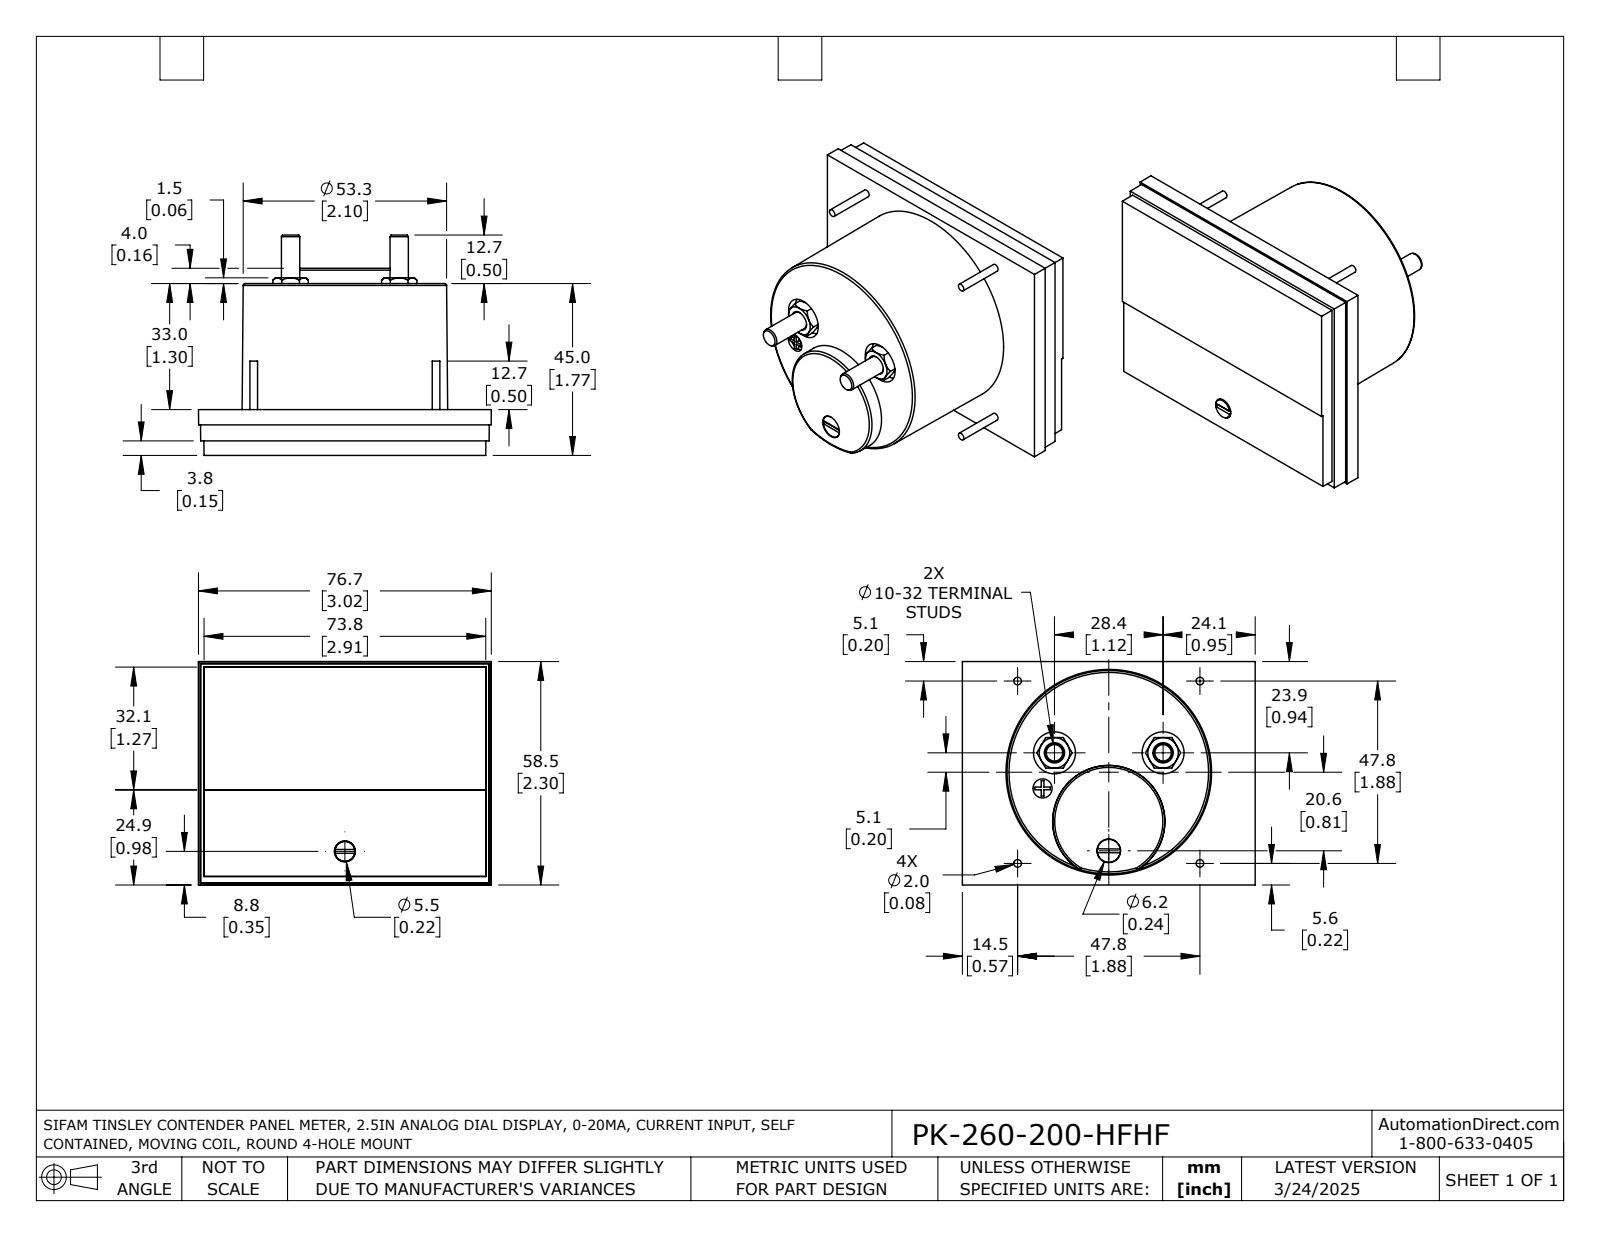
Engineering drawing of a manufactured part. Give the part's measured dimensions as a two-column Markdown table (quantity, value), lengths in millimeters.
| quantity | value |
| --- | --- |
| part name | PK-260-200-HFHF |
| STEP written by | SolidWorks 2021 (AUTOMOTIVE_DESIGN) |
| units | millimeters |
| bodies | 1 solid, 192 faces (95 planar, 37 cylindrical, 60 other) |
| overall size | 76.7 × 58.5 × 57.7 |
| volume | 125 500 mm³ |
| surface area | 23 580 mm² |
| round holes (diameter × count) | 5 × 3, 11 × 2, 5.3 × 1, 5.5 × 1, 6.2 × 1 |
| round bosses / shafts (diameter × count) | 2 × 4, 4.8 × 2, 6 × 1, 5.2 × 1 |
| partial cylindrical surfaces (radius × count) | 0.8 × 1 |
| main face-to-face distances | 0.5, 12, 3.3, 8.2, 3.8, 11.5, 1.4, 2, 10.1, 1.9 |
| hole center spacings | 29.3, 29.5, 9.8, 23.8, 23.9, 28.4, 32.9 |
